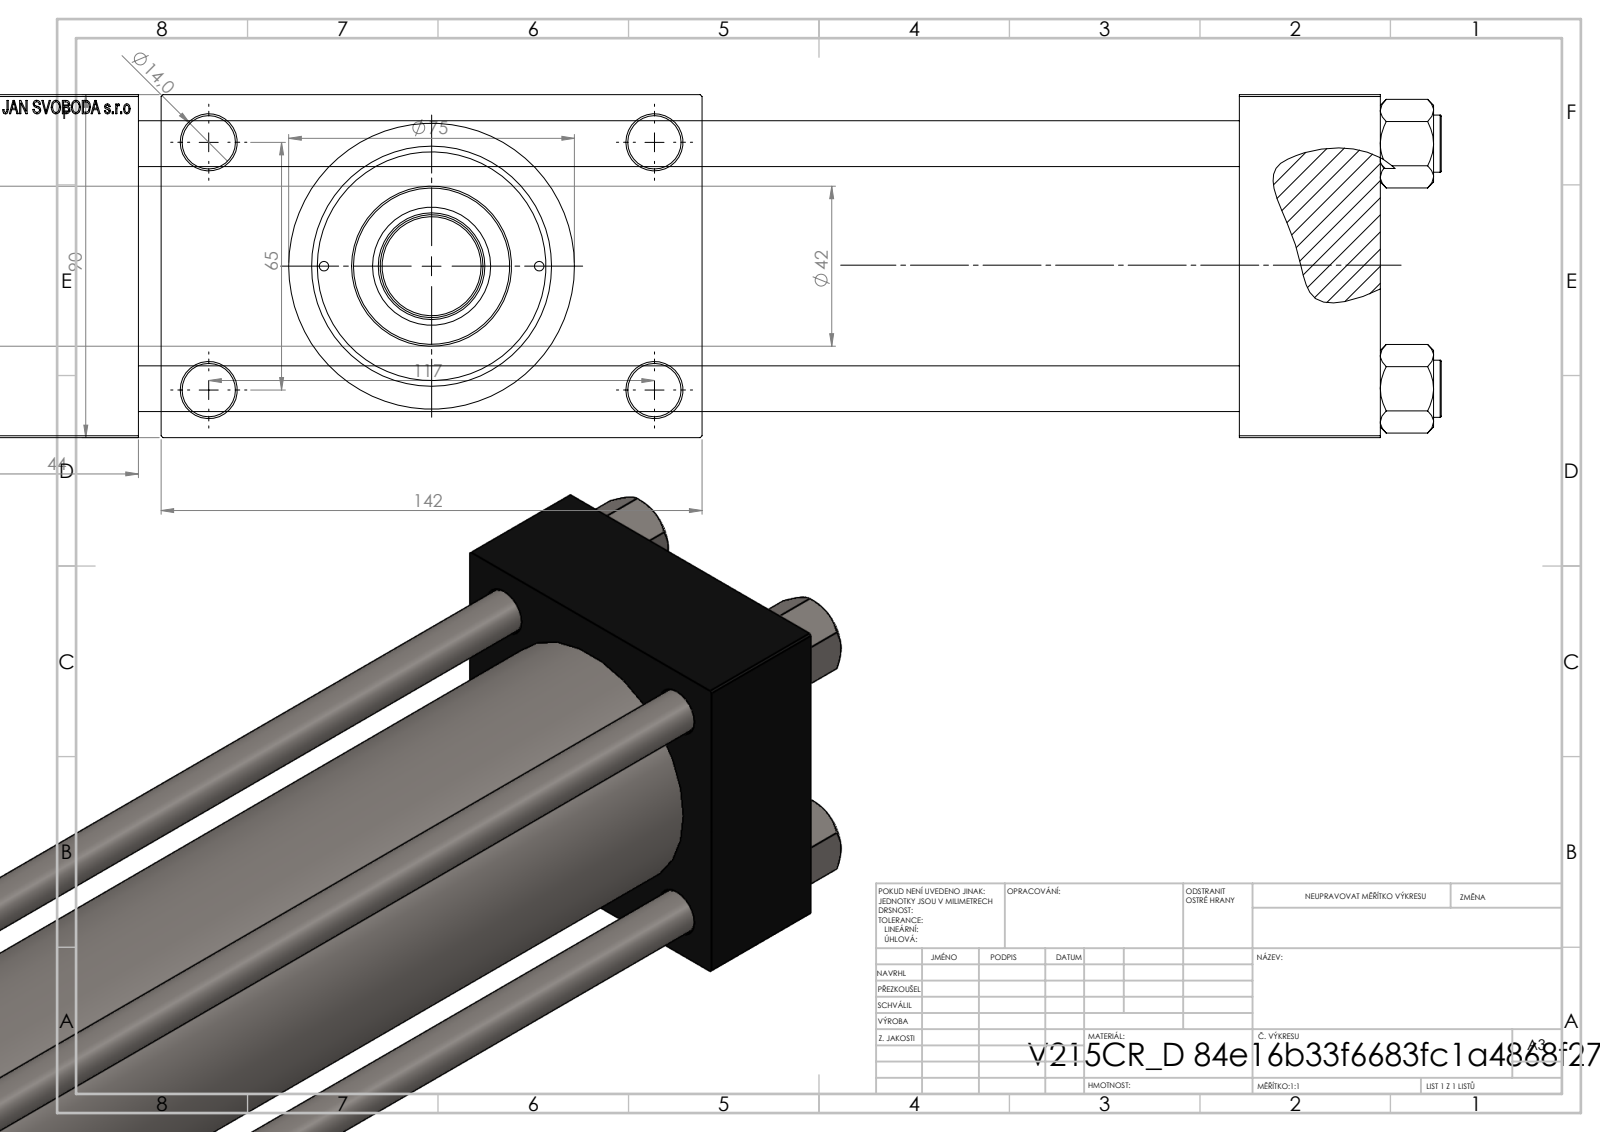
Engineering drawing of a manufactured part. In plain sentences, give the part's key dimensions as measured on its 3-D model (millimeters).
The part is named "V215CR_ROD_END_F; NUT_M5_D; V215CR_D_TYCINKA; V215CR_D_Body (+2 more)". Its 3-D file was written by "SolidWorks 2019 (CONFIG_CONTROL_DESIGN)". It is 12 solids with 1126 faces: 503 planar, 97 cylindrical and 526 other. Overall it measures 461 by 142 by 90 millimeters. Its volume is 1 505 000 cubic millimeters and its surface area 352 069 square millimeters. Round holes: 4 of diameter 12, 4 of diameter 14, 2 of diameter 2.5, 2 of diameter 7, 2 of diameter 20.96, 2 of diameter 30, 1 of diameter 18.5, 1 of diameter 28, 1 of diameter 31, 1 of diameter 50, 1 of diameter 60, 1 of diameter 63. Round bosses or shafts: 4 of diameter 15, 1 of diameter 75, 1 of diameter 69, 1 of diameter 42, 1 of diameter 27, 1 of diameter 18. The main face-to-face distances are 90, 289, 37, 326, 333, 370, 44, 26, 116, 142. The hole center spacings are 26.35, 32.39, 44.4, 45.47, 64.3, 66.92, 68.42, 69.81.
